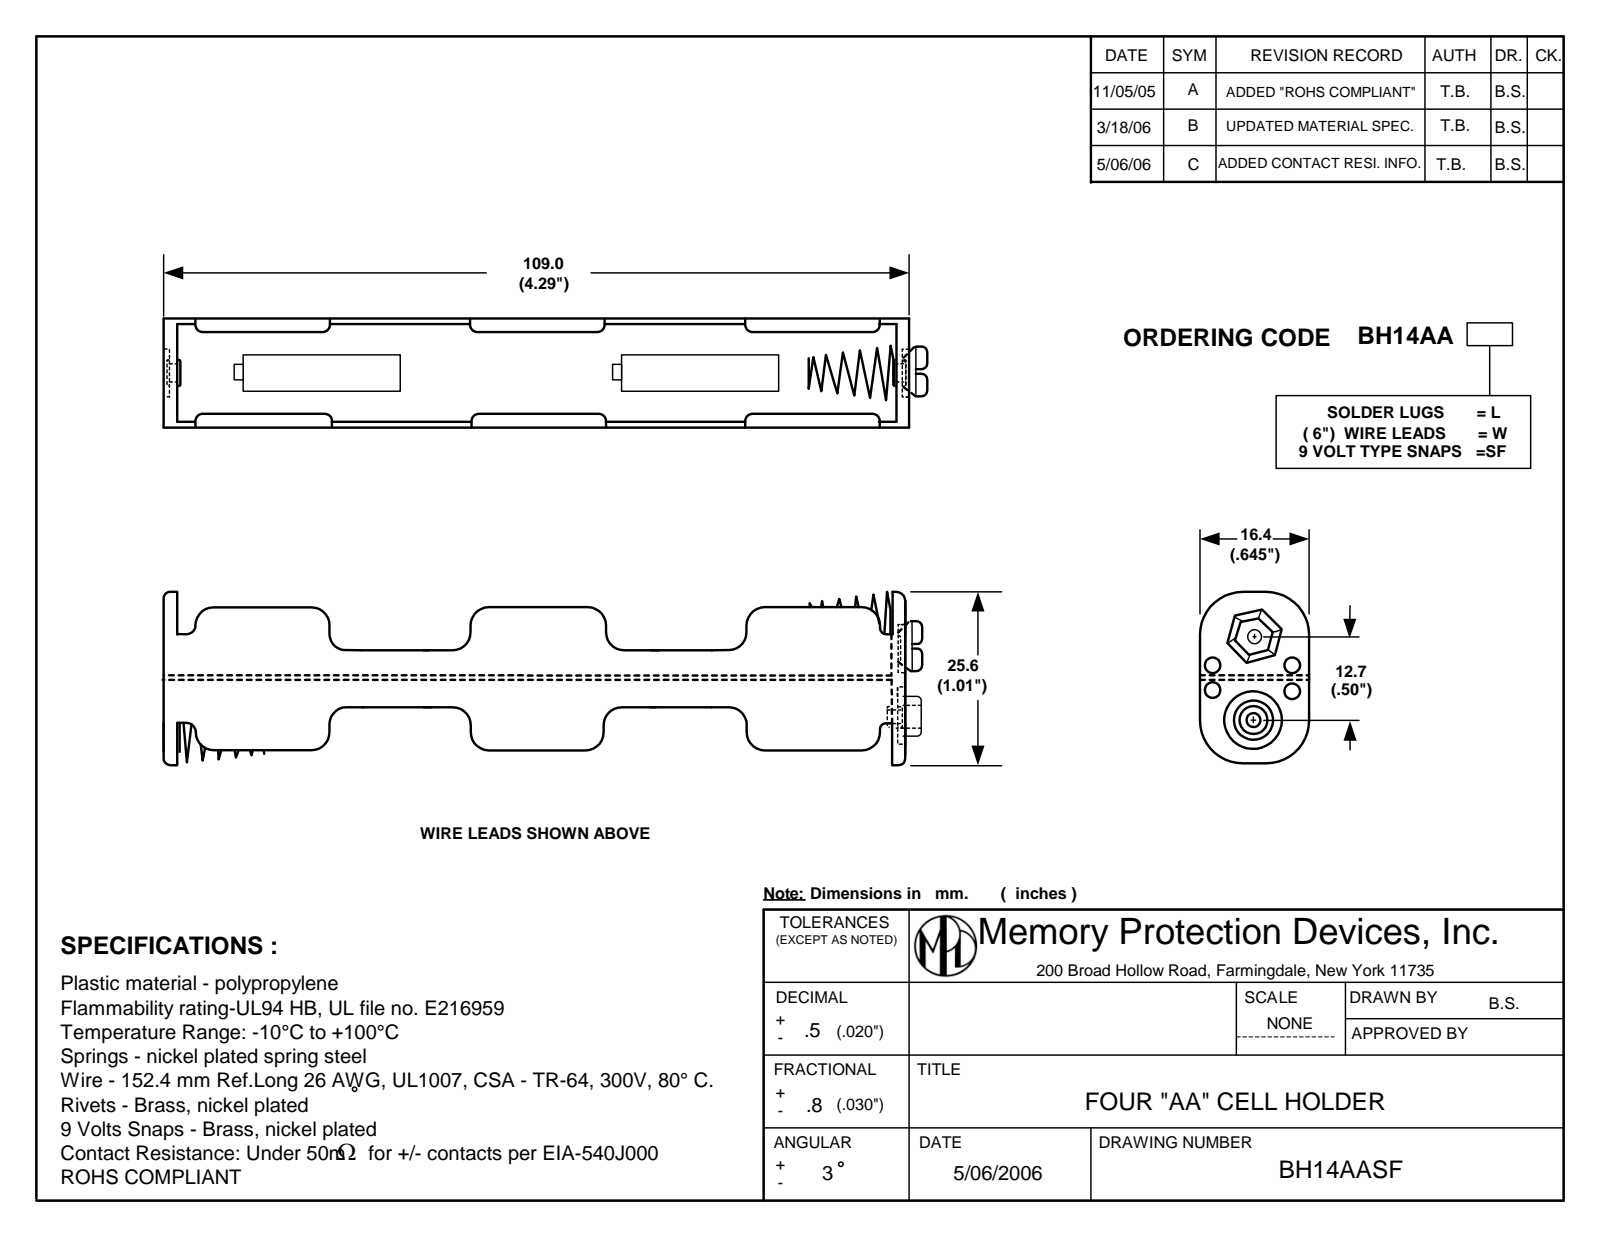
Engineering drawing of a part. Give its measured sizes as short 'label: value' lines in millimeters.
name: BH14AASF
written by: SolidWorks 2017 (AUTOMOTIVE_DESIGN)
unit: mm
bodies: 9 solids, 466 faces (234 planar, 172 cylindrical, 60 other)
size: 112.44 × 25.7 × 16.56
volume: 8 088 mm³; area: 14 360 mm²
holes: 2× ⌀2.54, 2× ⌀2.7, 2× ⌀3, 2× ⌀9.5, 1× ⌀4.95
bosses: 2× ⌀7, 2× ⌀6.2, 2× ⌀3.8, 2× ⌀0.63, 1× ⌀7.92, 1× ⌀5.71
rounds: 24× R2, 12× R0.25, 12× R0.38, 6× R0.76, 6× R0.89, 4× R2.5, 4× R5.45, 4× R9.22
face distances: 1.3, 15.26, 16.56, 13.96, 107.67, 0.99, 107.37, 106.37, 1, 107.36
hole spacings: 7.29, 10.13, 3.84, 12.9
